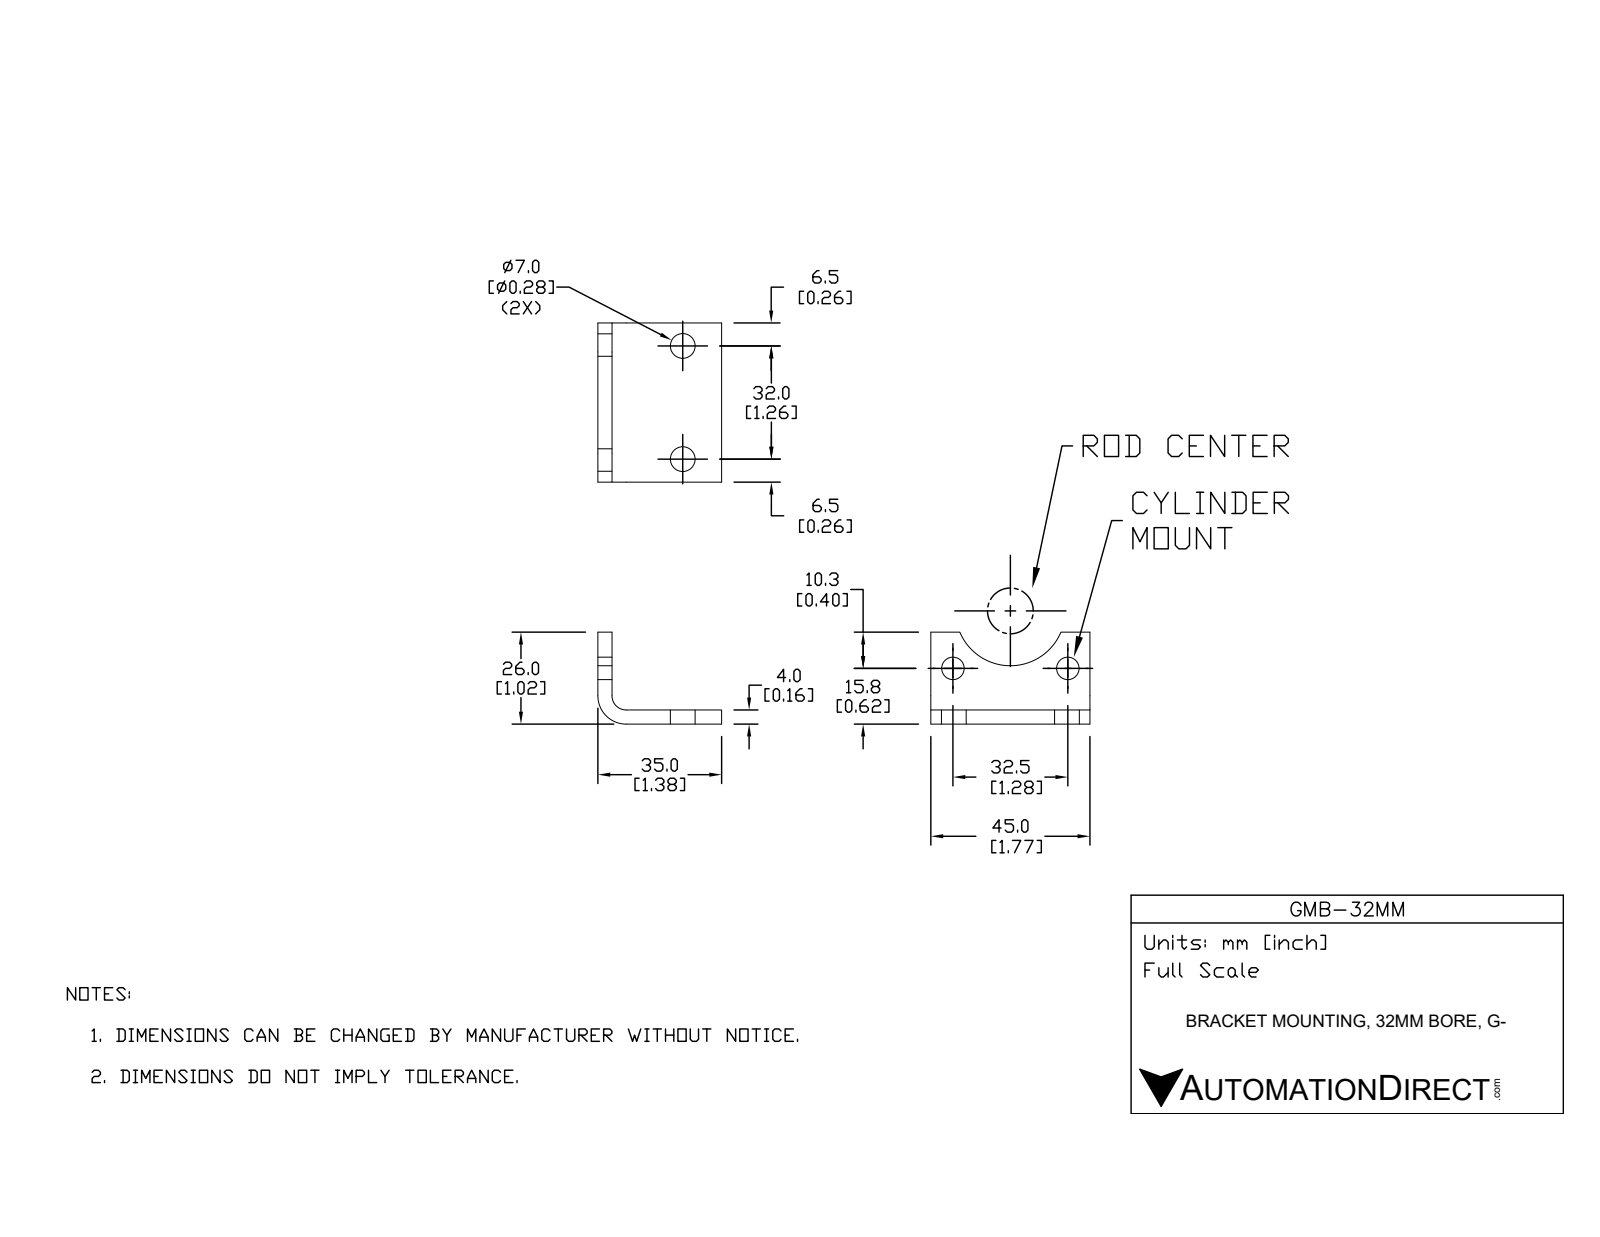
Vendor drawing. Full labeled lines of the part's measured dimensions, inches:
Part name (STEP PRODUCT): GMB-32MM
STEP written by: SolidWorks 2017 (AUTOMOTIVE_DESIGN)
Units: inches
Bodies: 1 solid, 24 faces (13 planar, 11 cylindrical, 0 other)
Overall size (bounding box): 1.772 × 1.378 × 1.024
Volume: 0.527 in³ · Surface area: 8.53 in²
Round holes (diameter × count): ⌀0.276 ×4
Partial cylindrical surfaces — rounded edges, fillets, slot ends (radius × count): R0.039 ×1, R0.197 ×1, R0.61 ×1
Main face-to-face distances: 0.157, 1.772, 1.378, 1.22, 1.024, 0.866
Hole centre spacings: 1.26, 1.28
